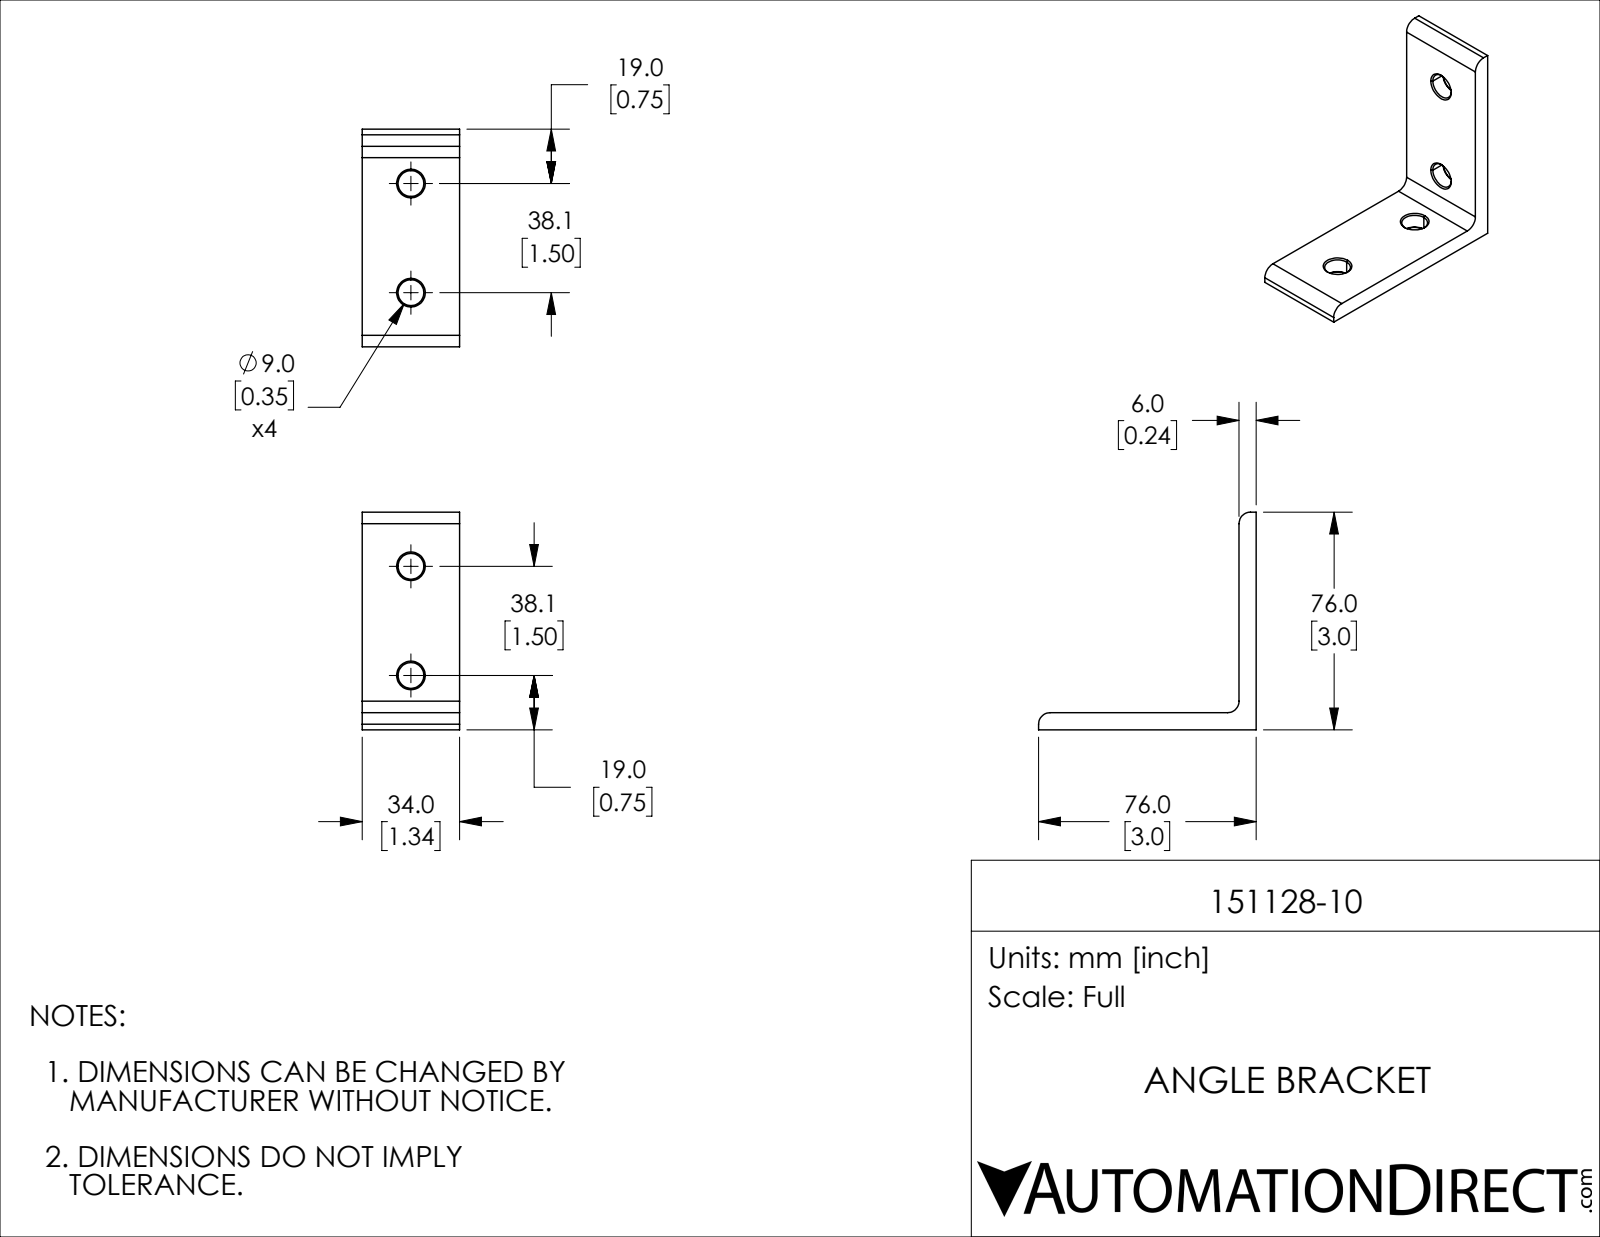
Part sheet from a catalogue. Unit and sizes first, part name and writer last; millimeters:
Units: millimetres
Overall size (bounding box): 76 × 76 × 34
Round holes (diameter × count): ⌀9 ×4
Partial cylindrical surfaces — rounded edges, fillets, slot ends (radius × count): R4 ×3
Main face-to-face distances: 6, 34, 76, 70
Hole centre spacings: 38.1
Volume: 28 111 mm³ · Surface area: 12 012 mm²
Bodies: 1 solid, 35 faces (8 planar, 11 cylindrical, 16 other)
Part name (STEP PRODUCT): 151128-10
STEP written by: SolidWorks 2024 (CONFIG_CONTROL_DESIGN)
